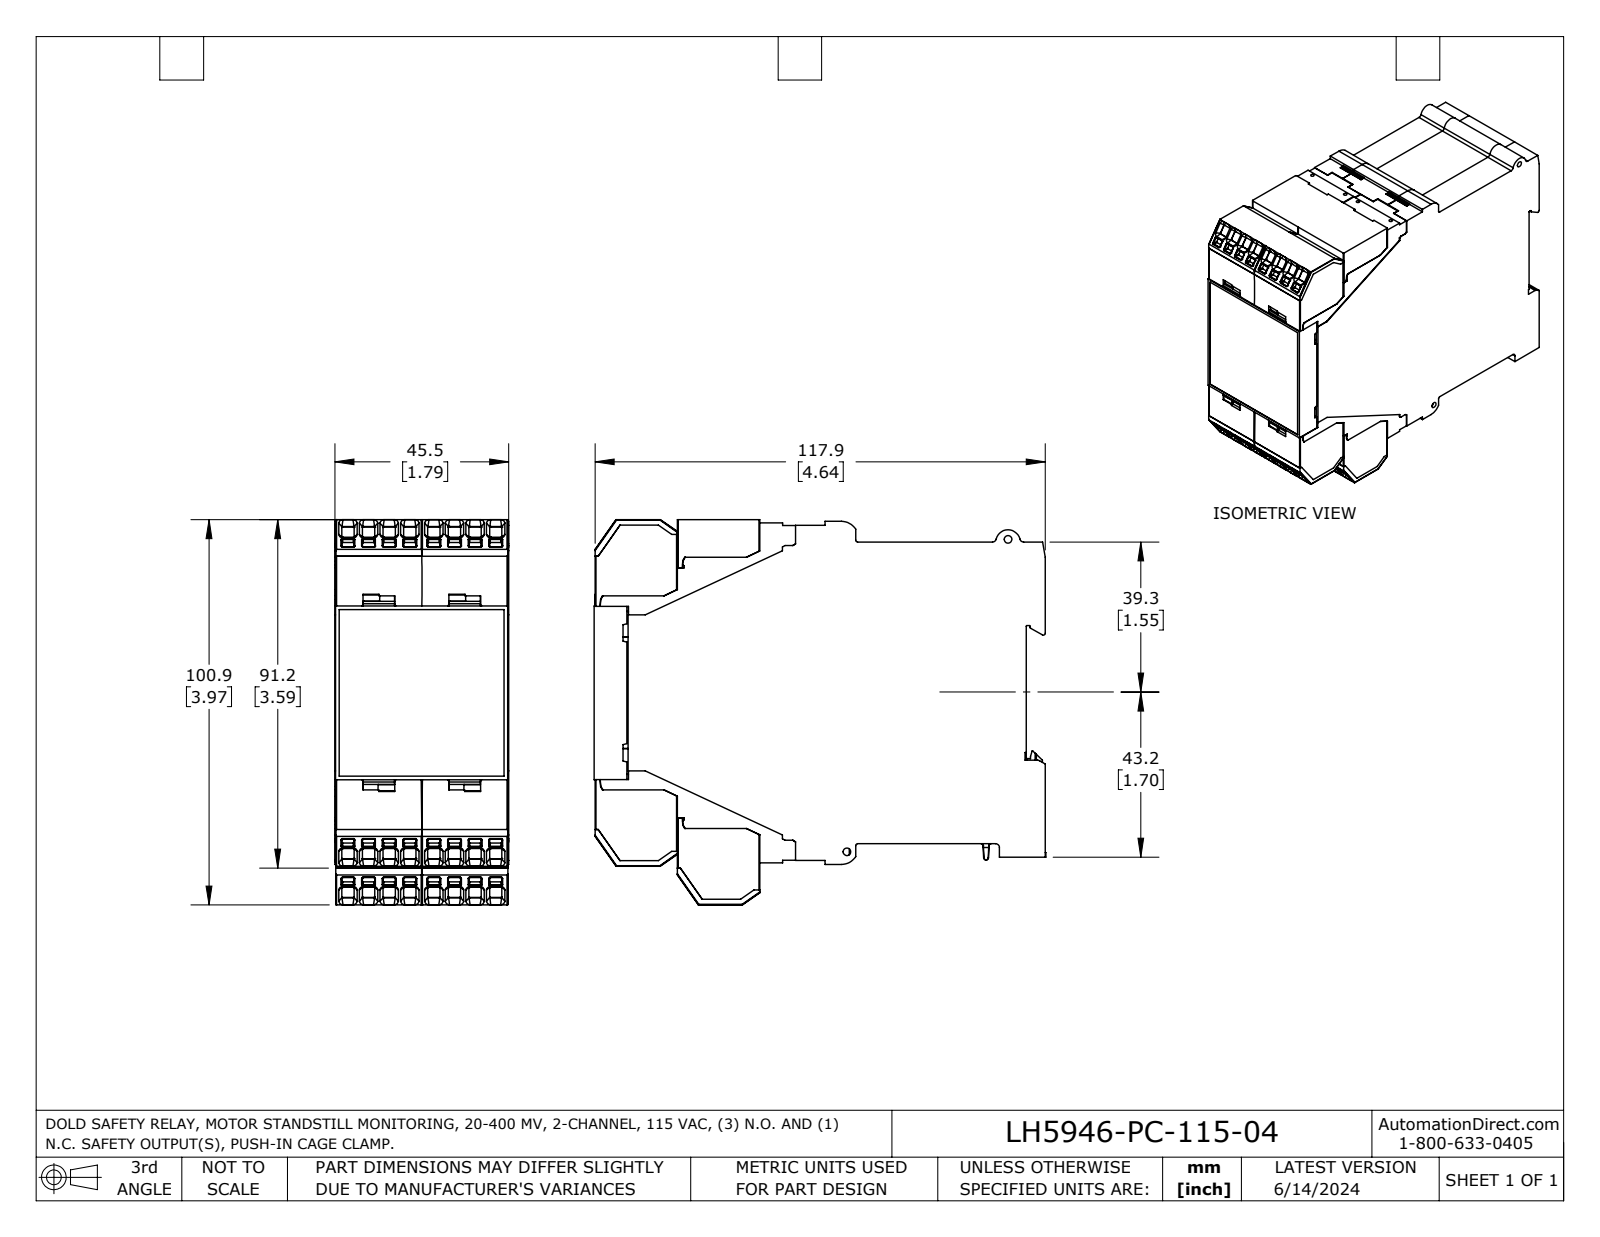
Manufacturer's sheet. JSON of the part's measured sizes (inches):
{"part_name": "LH5946_REV5", "step_written_by": "SolidWorks 2023 (AUTOMOTIVE_DESIGN)", "units": "inches", "bodies": {"solids": 1, "faces": 2563, "planar": 1515, "cylindrical": 811, "other": 237}, "overall_size": [4.699, 3.981, 1.791], "volume_in3": 27.53, "surface_area_in2": 76.02, "round_holes": [[0.047, 8], [0.079, 3], [0.079, 1], [0.079, 1]], "round_bosses_or_shafts": [[0.039, 4], [0.087, 1]], "partial_cylinders_radius": [[0.008, 315], [0.039, 32], [0.02, 25], [0.015, 4], [0.012, 3], [0.174, 2], [0.022, 1], [0.043, 1]], "face_to_face_distances": [1.791, 1.783, 4.454, 1.776, 3.11, 0.23, 3.34, 1.785, 1.778, 0.026], "hole_center_spacings": [0.638, 0.886, 0.248, 1.524, 0.712, 1.662, 1.663, 2.07]}
